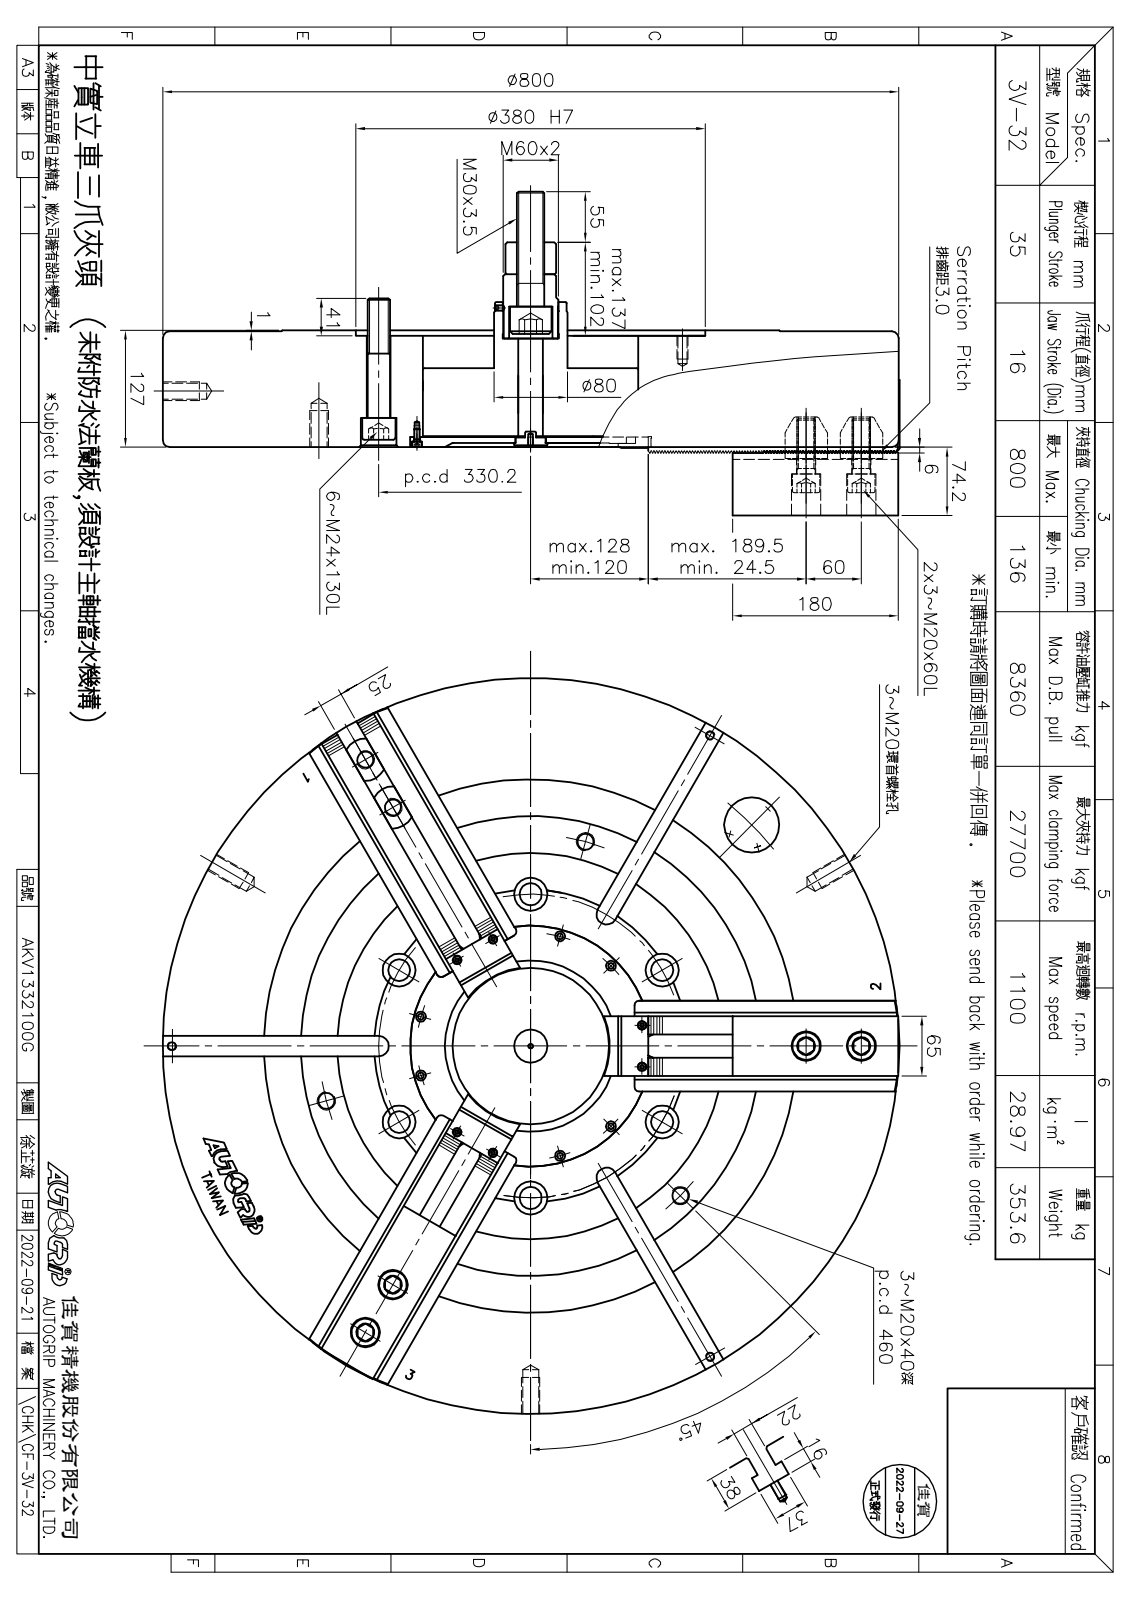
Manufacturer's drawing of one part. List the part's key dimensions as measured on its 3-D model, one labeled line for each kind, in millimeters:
Part name (STEP PRODUCT): CF-3V-32; CF-3H-221-04000(T型塊); 圓頭內六角螺栓_M30x125(全牙); CF-3P-15-05000 (+8 more)
STEP written by: SolidWorks 2016 (CONFIG_CONTROL_DESIGN)
Units: millimetres
Bodies: 40 solids, 6173 faces (4736 planar, 1115 cylindrical, 322 other)
Overall size (bounding box): 801 × 800 × 352.2
Volume: 63 180 000 mm³ · Surface area: 2 760 000 mm²
Round holes (diameter × count): ⌀17.5 ×12, ⌀5 ×7, ⌀6.6 ×6, ⌀11 ×6, ⌀21 ×6, ⌀26 ×6, ⌀32 ×6, ⌀39 ×6, ⌀10.2 ×3, ⌀27 ×1, ⌀30 ×1, ⌀33 ×1
Round bosses / shafts (diameter × count): ⌀36 ×7, ⌀30 ×6, ⌀24 ×6, ⌀20 ×6, ⌀10 ×6, ⌀6 ×6, ⌀800 ×1, ⌀80 ×1
Partial cylindrical surfaces — rounded edges, fillets, slot ends (radius × count): R0.1 ×423, R23 ×6, R11 ×3, R12.5 ×3, R18.5 ×3, R400 ×3, R112 ×1, R131 ×1
Main face-to-face distances: 126, 65, 1, 127, 115, 6, 20, 48, 45, 11
Hole centre spacings: 165.1, 123.5, 176.95, 178.76, 229.44, 285.96, 341.99, 395.6
